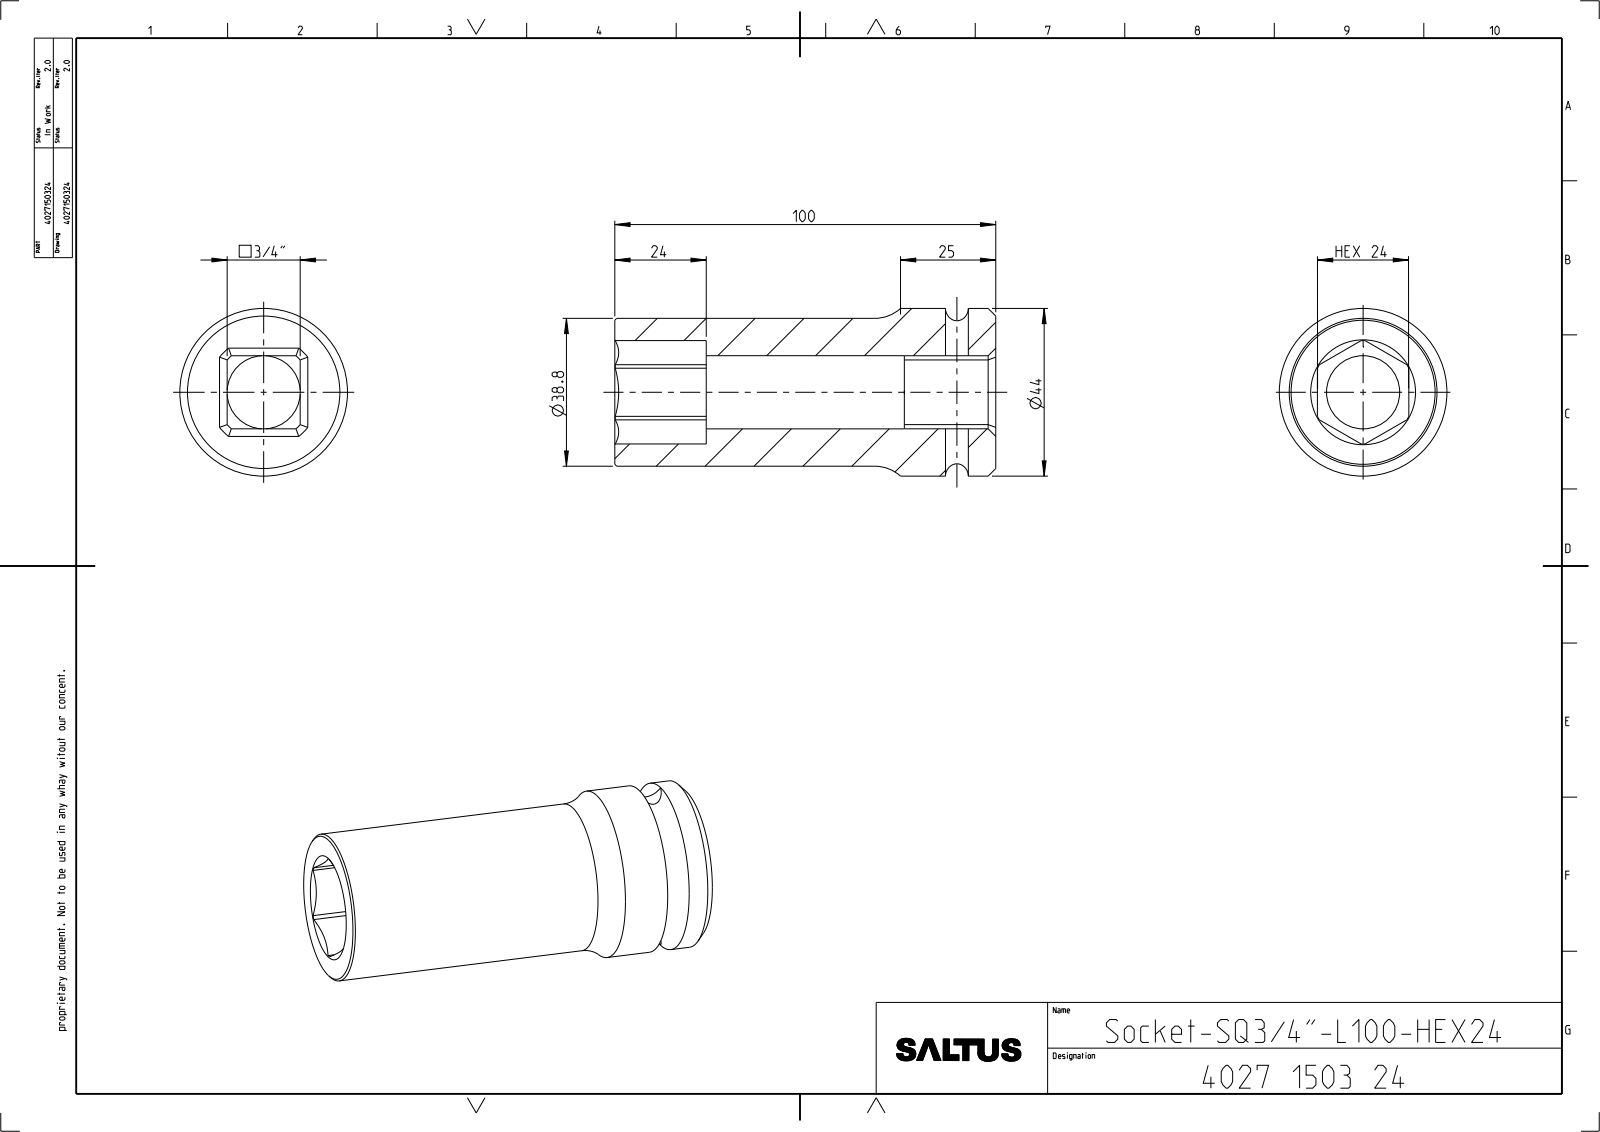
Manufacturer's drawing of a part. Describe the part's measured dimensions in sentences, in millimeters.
The part is named "4027150324". Its 3-D file was written by "CREO PARAMETRIC BY PTC INC, 2022414 (CONFIG_CONTROL_DESIGN)". It is 1 solid with 61 faces: 21 planar, 22 cylindrical and 18 other. Overall it measures 100 by 44 by 44 millimeters. Its volume is 88 743 cubic millimeters and its surface area 22 028 square millimeters. Round holes: 1 of diameter 6, 1 of diameter 19.2. Round bosses or shafts: 1 of diameter 44, 1 of diameter 38.8. Partial cylindrical surfaces (rounded edges, fillets, slot ends): 1 of radius 12.8, 1 of radius 13.56. The main face-to-face distances are 24, 19.18, 2.41, 21.59, 100, 76, 52.
